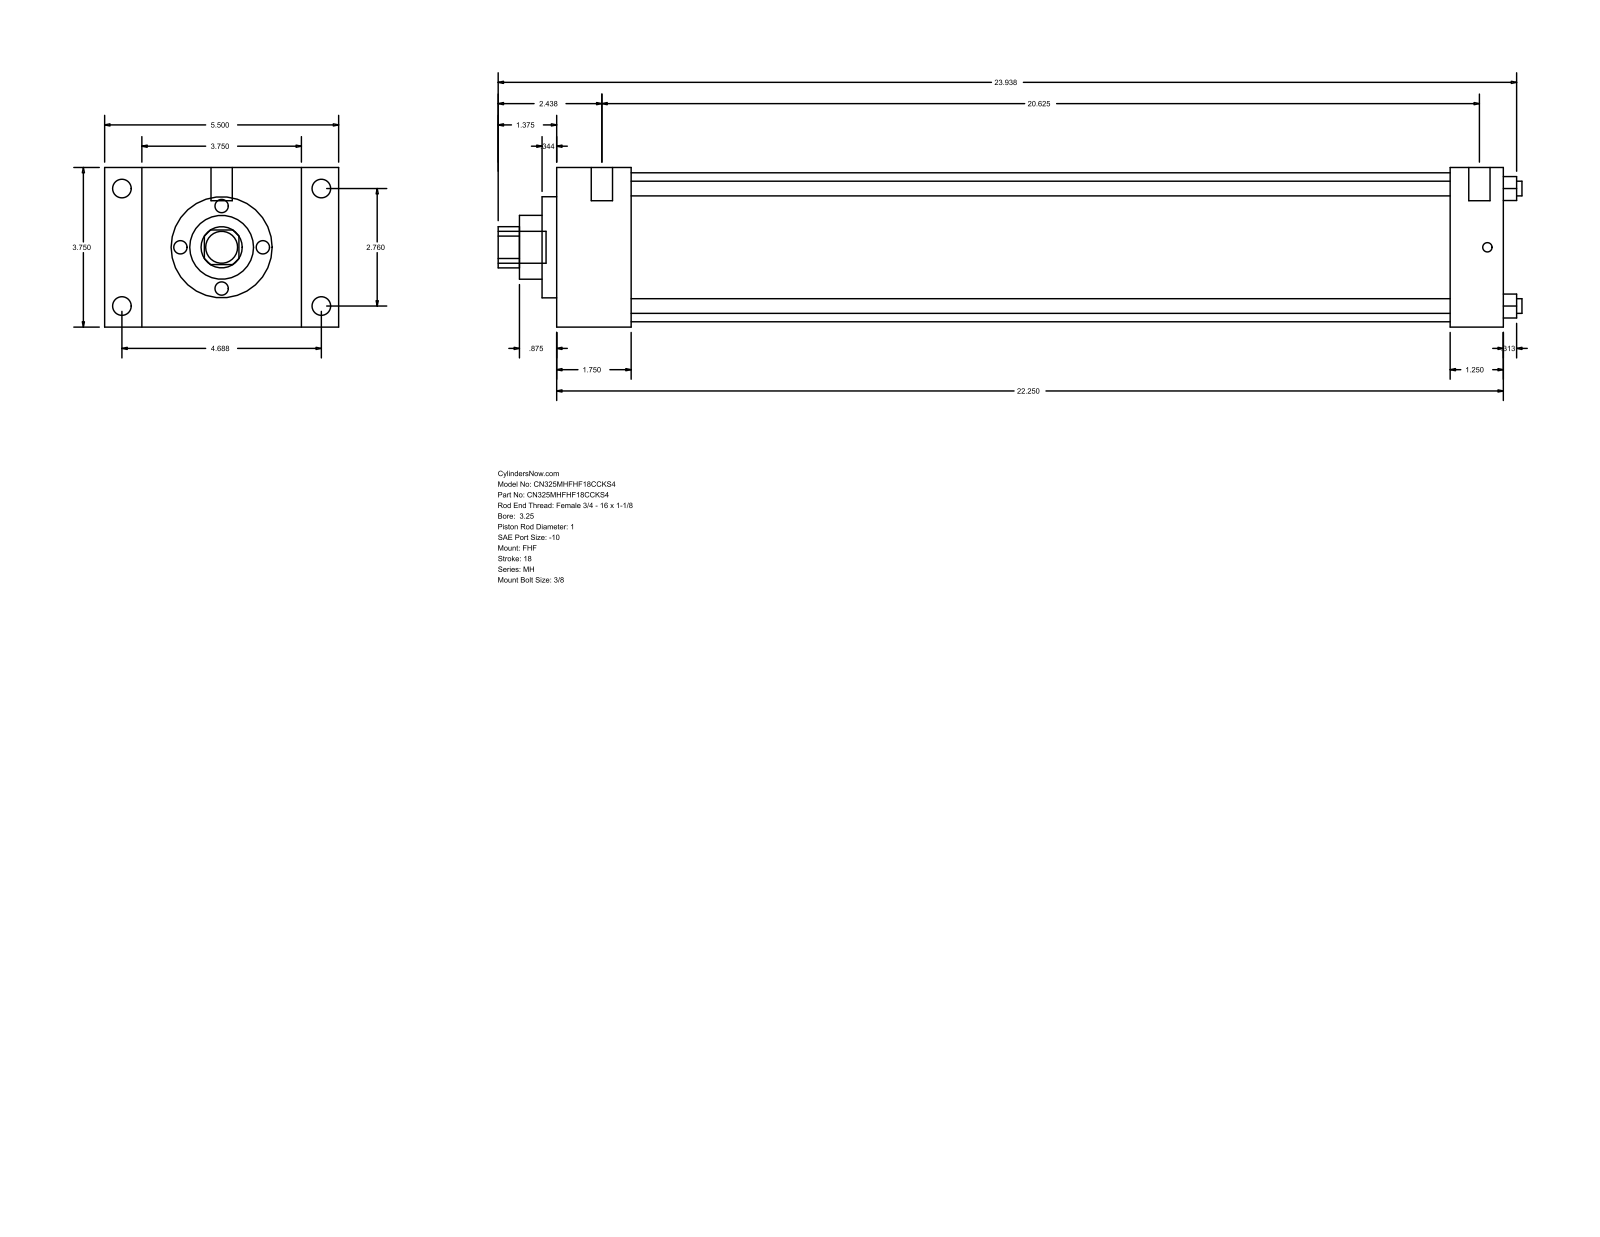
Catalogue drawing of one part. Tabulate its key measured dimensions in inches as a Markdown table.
| quantity | value |
| --- | --- |
| part name | MH_FHF__0325_1 |
| STEP written by | GSSL Pune (CONFIG_CONTROL_DESIGN) |
| units | inches |
| bodies | 0 solids, 90 faces (61 planar, 29 cylindrical, 0 other) |
| overall size | 24.063 × 5.5 × 3.75 |
| round holes (diameter × count) | 0.345 × 4, 1 × 1, 1.5 × 1, 2.375 × 1, 3.5 × 1 |
| round bosses / shafts (diameter × count) | 0.438 × 4, 0.219 × 4, 0.5 × 2, 0.75 × 1 |
| partial cylindrical surfaces (radius × count) | 0.484 × 1 |
| main face-to-face distances | 3.75, 22.25, 1.75, 20.5, 0.875, 4.625, 5.5, 21, 19.25, 1.25 |
| hole center spacings | 1.952, 2.76, 3.903 |
